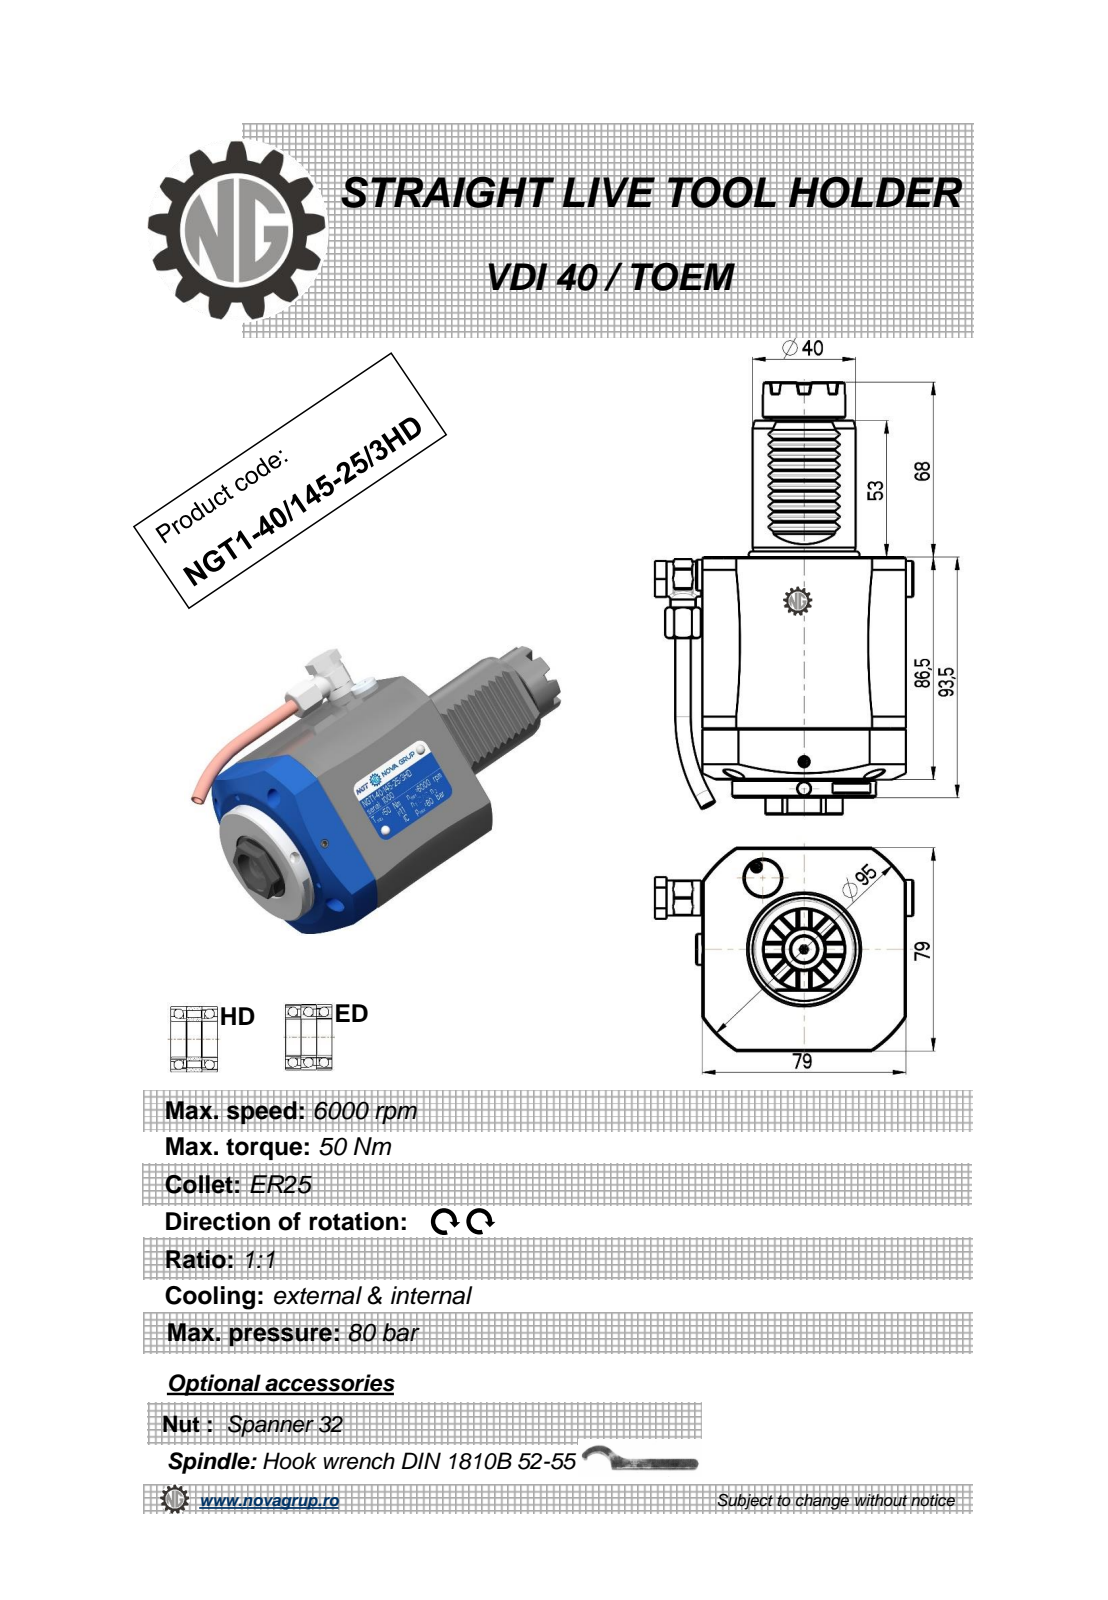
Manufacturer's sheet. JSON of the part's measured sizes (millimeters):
{"part_name": "NGT1_40_145_25_3HD", "step_written_by": "PRO/ENGINEER BY PARAMETRIC TECHNOLOGY CORPORATION, 2010280 (CONFIG_CONTROL_DESIGN)", "units": "millimeters", "bodies": {"solids": 3, "faces": 460, "planar": 192, "cylindrical": 109, "other": 159}, "overall_size": [168, 100.4, 79], "volume_mm3": 600127, "surface_area_mm2": 54499, "round_holes": [[4, 3], [5, 2], [3, 1], [6, 1], [6.2, 1], [9, 1], [10, 1], [11, 1], [18, 1], [26.5, 1]], "round_bosses_or_shafts": [[56, 1], [40, 1], [32, 1], [17.2, 1], [14, 1], [13.6, 1], [13, 1], [12, 1]], "partial_cylinders_radius": [[0.3, 10], [0.41, 6], [0.5, 4], [7.7, 1], [15, 1], [47, 1], [47.5, 1]], "face_to_face_distances": [79, 86.5, 7, 93.5, 2.83, 53, 146.5, 139.5, 8.48, 14.14], "hole_center_spacings": [0.4, 51.08, 51.45, 83.92]}
